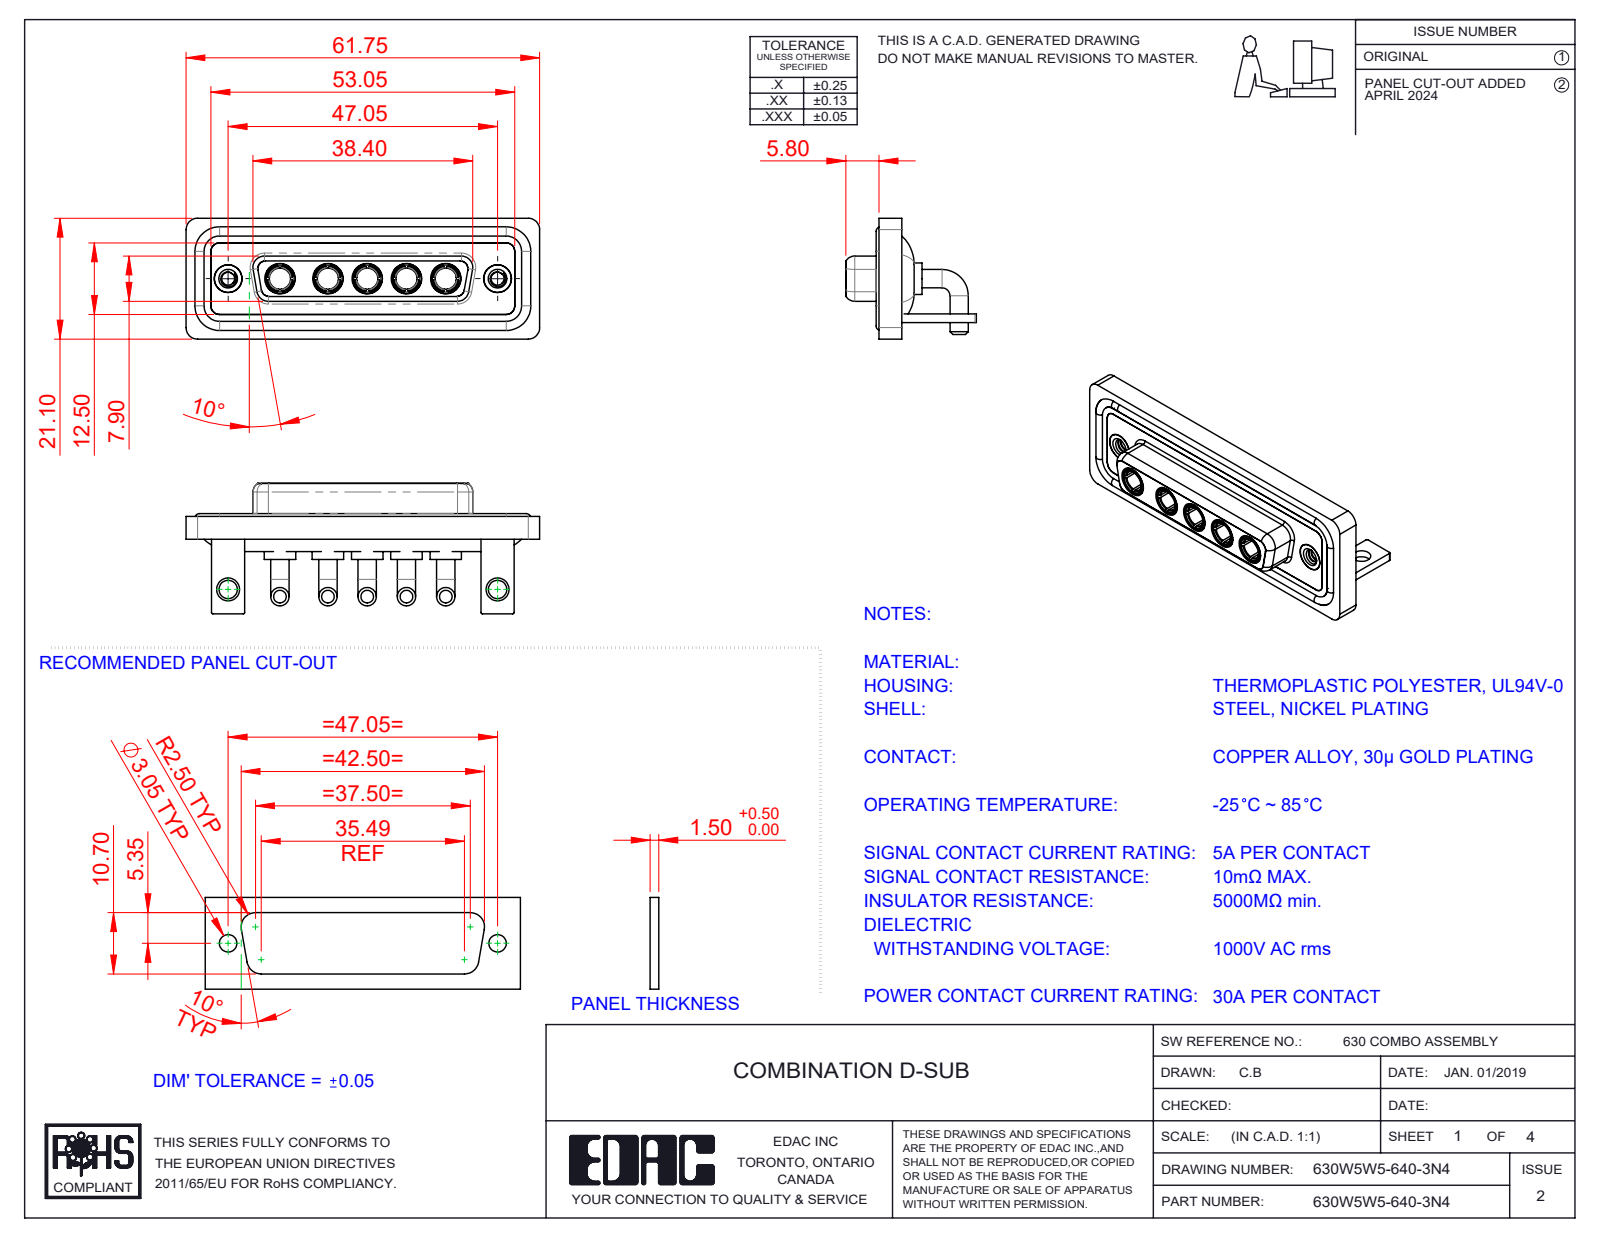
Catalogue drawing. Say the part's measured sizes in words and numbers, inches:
The part is named "630Combo Housing_5W5; Power Socket_30A RA; 630Combo Shell Front_25 Contacts; 630Combo Shell Rear_25 Contacts (+4 more)". Its 3-D file was written by "SolidWorks 2023 (CONFIG_CONTROL_DESIGN)". It is 19 solids with 824 faces: 270 planar, 337 cylindrical and 217 other. Overall it measures 2.431 by 0.898 by 0.831 inches. Its volume is 0.546 cubic inches and its surface area 22.69 square inches. Round holes: 7 of diameter 0.191, 5 of diameter 0.146, 5 of diameter 0.209, 2 of diameter 0.089, 2 of diameter 0.126, 2 of diameter 0.157, 2 of diameter 0.159, 2 of diameter 0.197. Round bosses or shafts: 10 of diameter 0.126, 5 of diameter 0.217, 5 of diameter 0.205, 5 of diameter 0.195, 5 of diameter 0.187, 5 of diameter 0.148, 4 of diameter 0.063, 2 of diameter 0.195. Partial cylindrical surfaces (rounded edges, fillets, slot ends): 19 of radius 0.079, 18 of radius 0.059, 16 of radius 0.01, 8 of radius 0.053, 8 of radius 0.063, 5 of radius 0.02, 5 of radius 0.083, 4 of radius 0.024. The main face-to-face distances are 0.016, 0.071, 0.114, 0.146, 0.059, 0.161, 0.043, 0.055, 0.063, 0.098. The hole center spacings are 0.27, 0.356, 1.496, 1.852, 0.27, 0.33, 0.54, 0.541.
